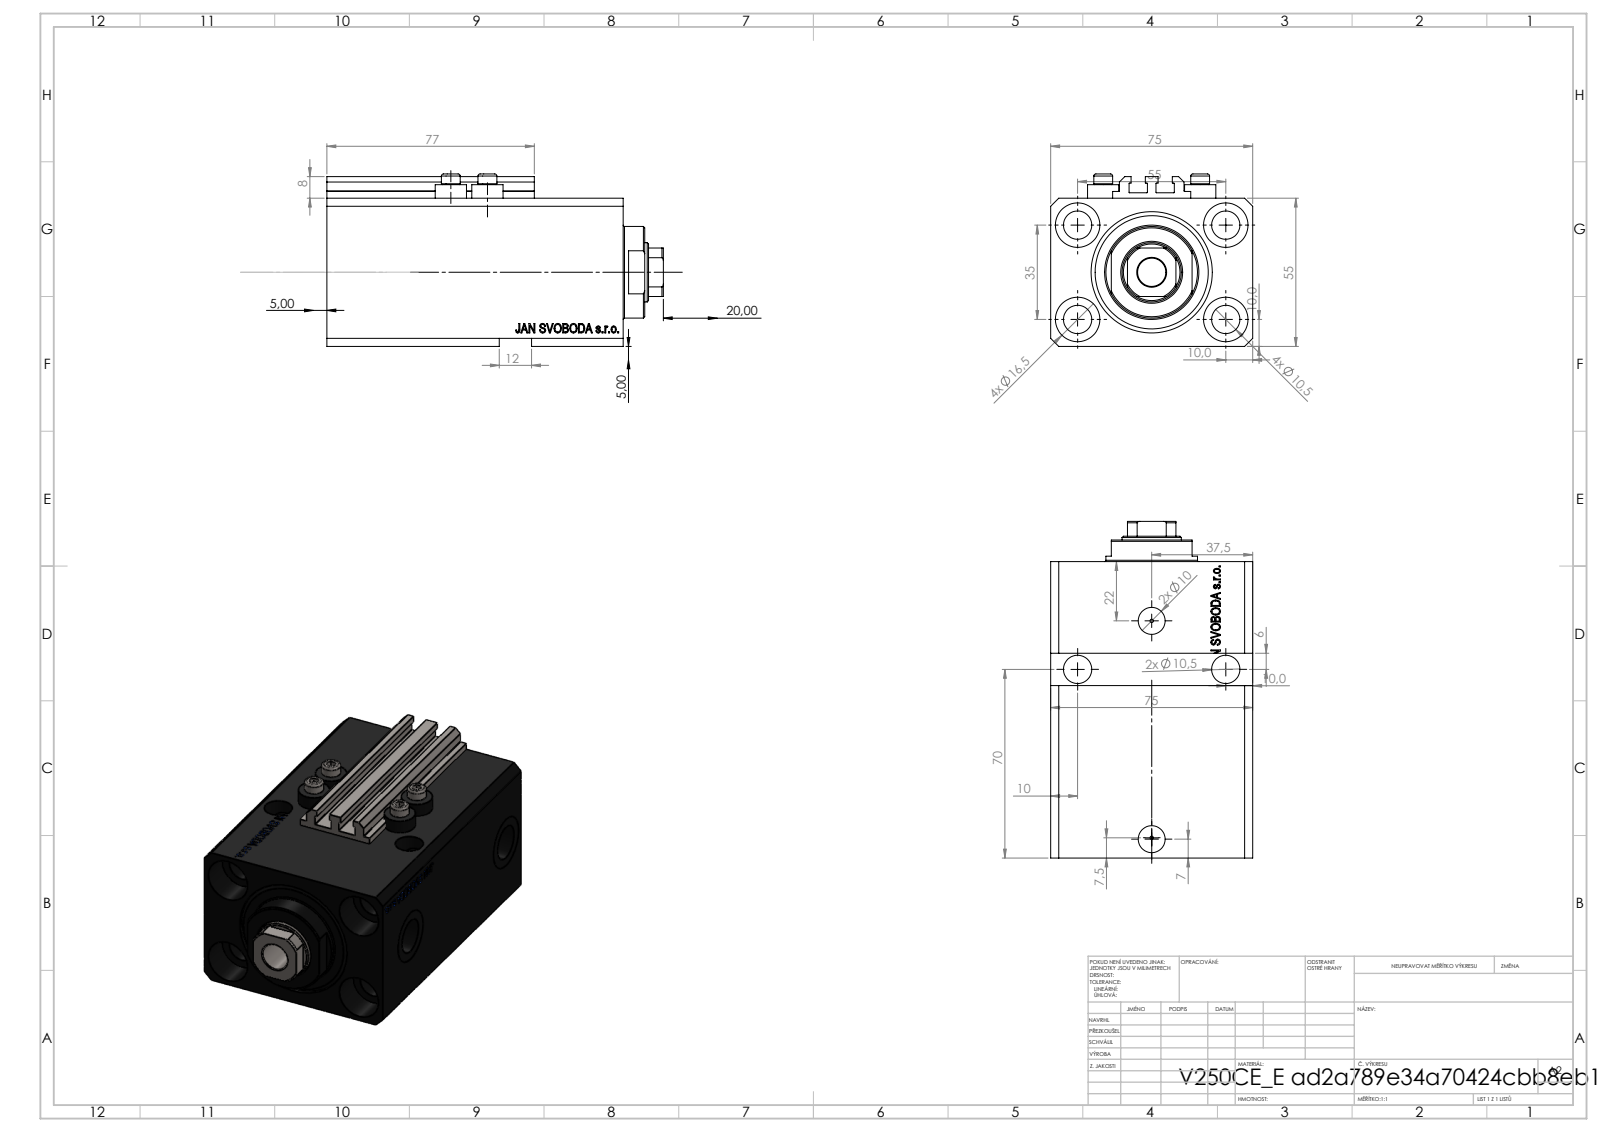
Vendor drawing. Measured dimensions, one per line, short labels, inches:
name: ALLEN BOLT V250CE; V250CE_E_Body; V250CE_VC_E; V250CE_C_VCP
written by: SolidWorks 2019 (CONFIG_CONTROL_DESIGN)
unit: in
bodies: 8 solids, 1084 faces (514 planar, 146 cylindrical, 424 other)
size: 4.921 × 2.953 × 2.52
volume: 23.27 in³; area: 148.2 in²
holes: 9× ⌀0.413, 4× ⌀0.049, 4× ⌀0.157, 4× ⌀0.65, 2× ⌀0.394, 2× ⌀0.518, 2× ⌀0.787, 1× ⌀0.866, 1× ⌀1.26, 1× ⌀1.772
bosses: 4× ⌀0.457, 4× ⌀0.276, 1× ⌀1.339
rounds: 10× R0.008, 1× R0.413
face distances: 2.165, 2.953, 0.591, 4.331, 3.74, 0.118, 0.39, 3.35, 3.941, 2.244
hole spacings: 1.283, 1.294, 2.165, 2.706, 0.535, 0.555, 0.907, 1.016
